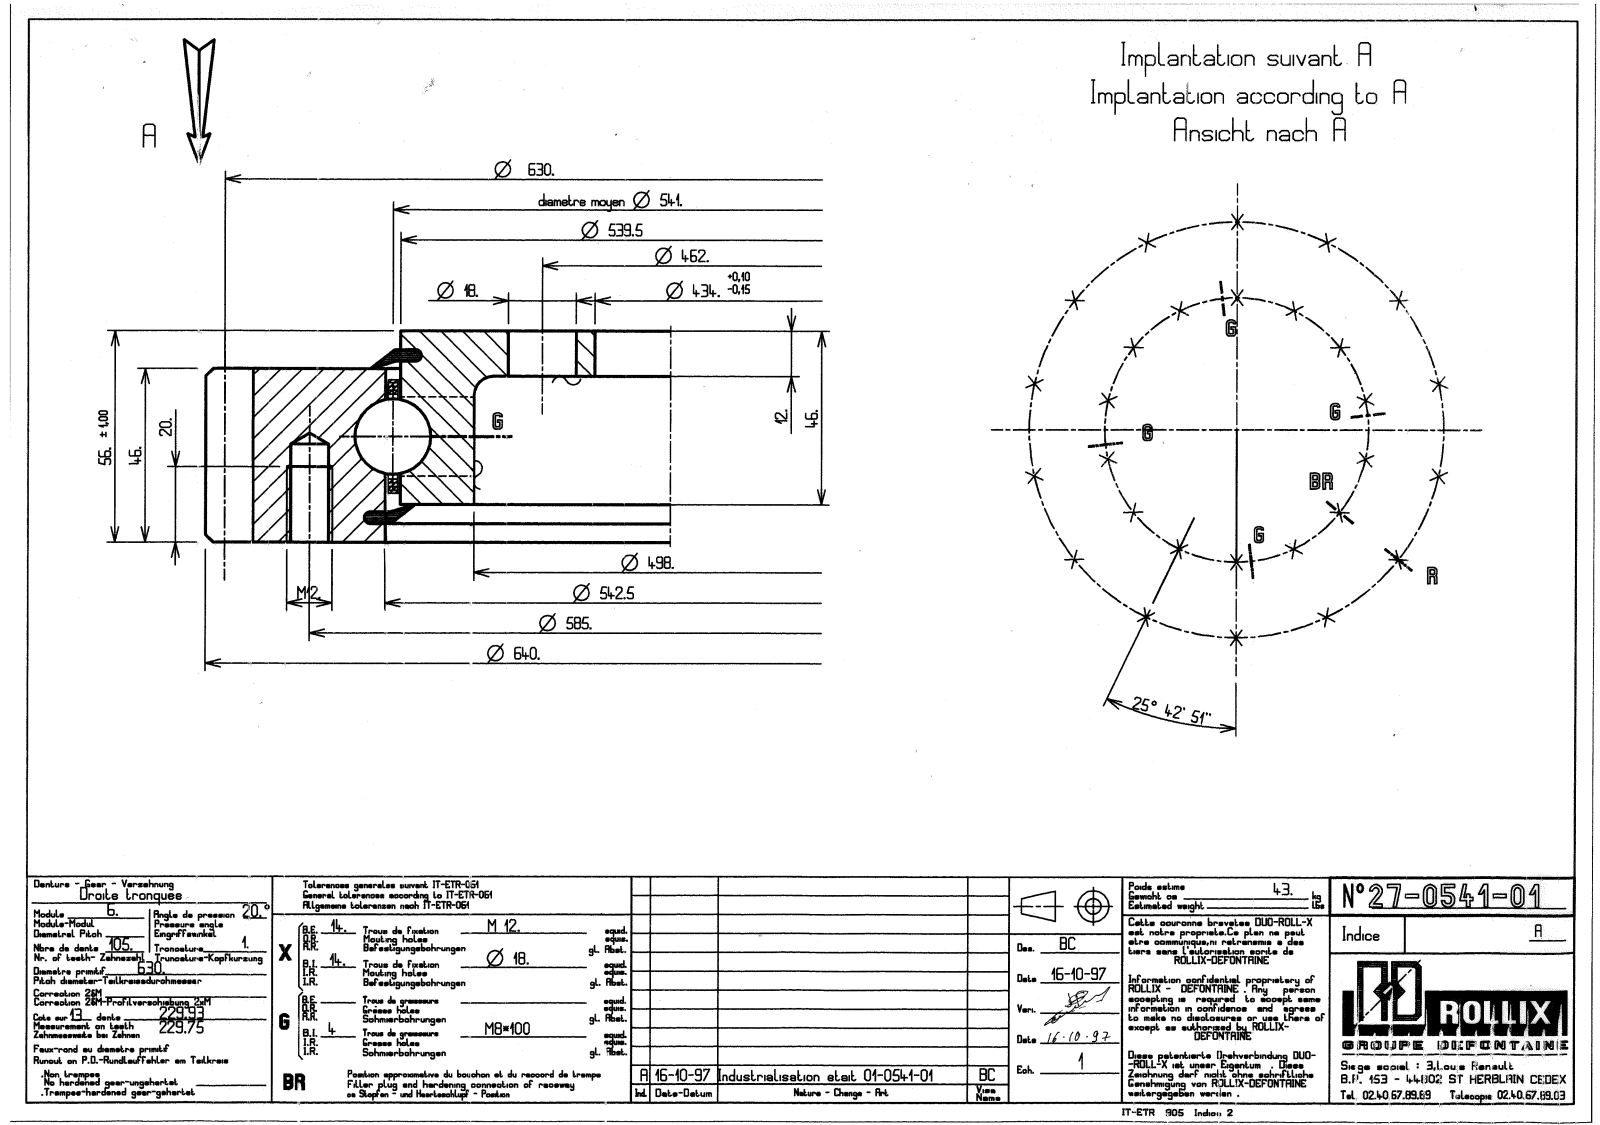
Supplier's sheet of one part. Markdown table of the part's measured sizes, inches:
| quantity | value |
| --- | --- |
| part name | 21-0541-01 |
| STEP written by | SolidWorks 2016 (CONFIG_CONTROL_DESIGN) |
| units | inches |
| bodies | 9 solids, 871 faces (263 planar, 299 cylindrical, 309 other) |
| overall size | 25.196 × 25.194 × 2.205 |
| volume | 315 in³ |
| surface area | 1 365 in² |
| round holes (diameter × count) | 0.404 × 14, 0.709 × 14, 0.276 × 4, 17.087 × 1, 19.606 × 1, 21.476 × 1 |
| round bosses / shafts (diameter × count) | 0.315 × 4, 21.122 × 1 |
| partial cylindrical surfaces (radius × count) | 12.106 × 1, 12.598 × 1 |
| main face-to-face distances | 0.394, 1.811, 2.205, 1.732, 0.079, 0.472, 1.339, 1.417, 0.317, 1.888 |
| hole center spacings | 16.184, 20.101, 5.158, 9.205, 12.989, 18.599, 2.421, 9.094 |
